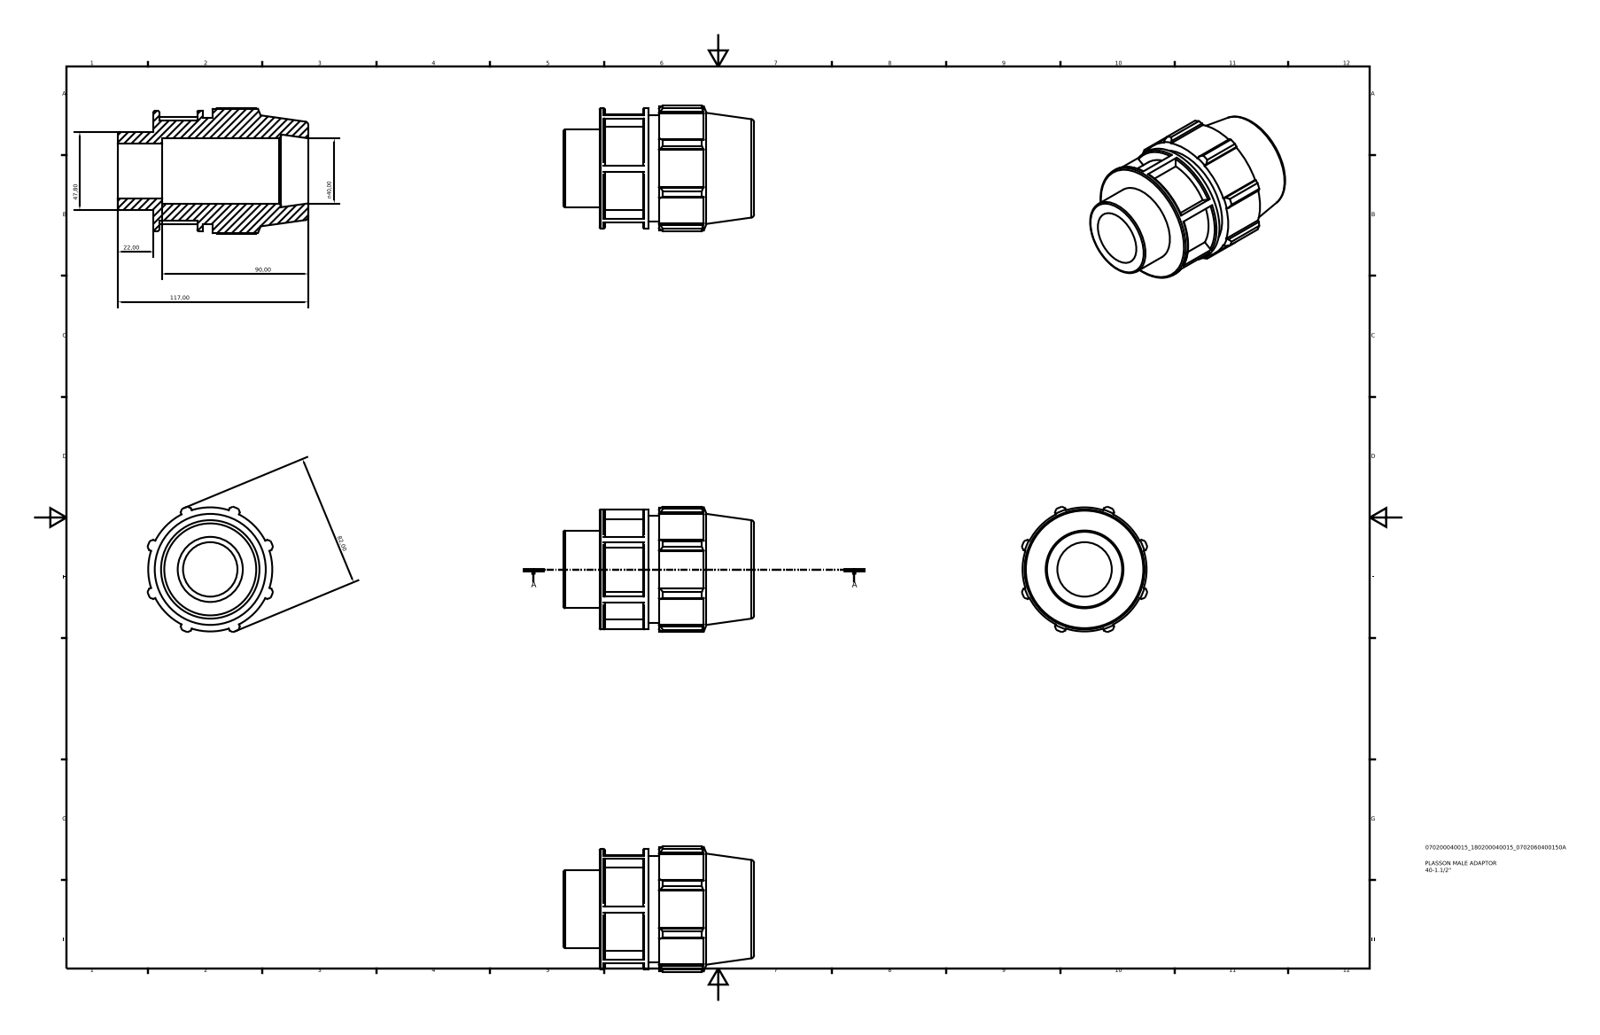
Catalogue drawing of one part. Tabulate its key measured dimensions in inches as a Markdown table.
| quantity | value |
| --- | --- |
| part name | 070200040015_180200040015 |
| STEP written by | Autodesk Inventor 2015 (AUTOMOTIVE_DESIGN) |
| units | inches |
| bodies | 1 solid, 117 faces (63 planar, 27 cylindrical, 27 other) |
| overall size | 4.606 × 3.038 × 3.038 |
| volume | 15.5 in³ |
| surface area | 78.92 in² |
| round holes (diameter × count) | 1.317 × 1, 1.575 × 1 |
| round bosses / shafts (diameter × count) | 2.906 × 1, 2.583 × 1, 2.421 × 1, 1.882 × 1 |
| partial cylindrical surfaces (radius × count) | 1.501 × 1, 1.614 × 1 |
| main face-to-face distances | 2.303, 3.74, 1.437, 1.053, 0.384, 2.687, 0.131, 0.921, 1.306, 3.609 |
